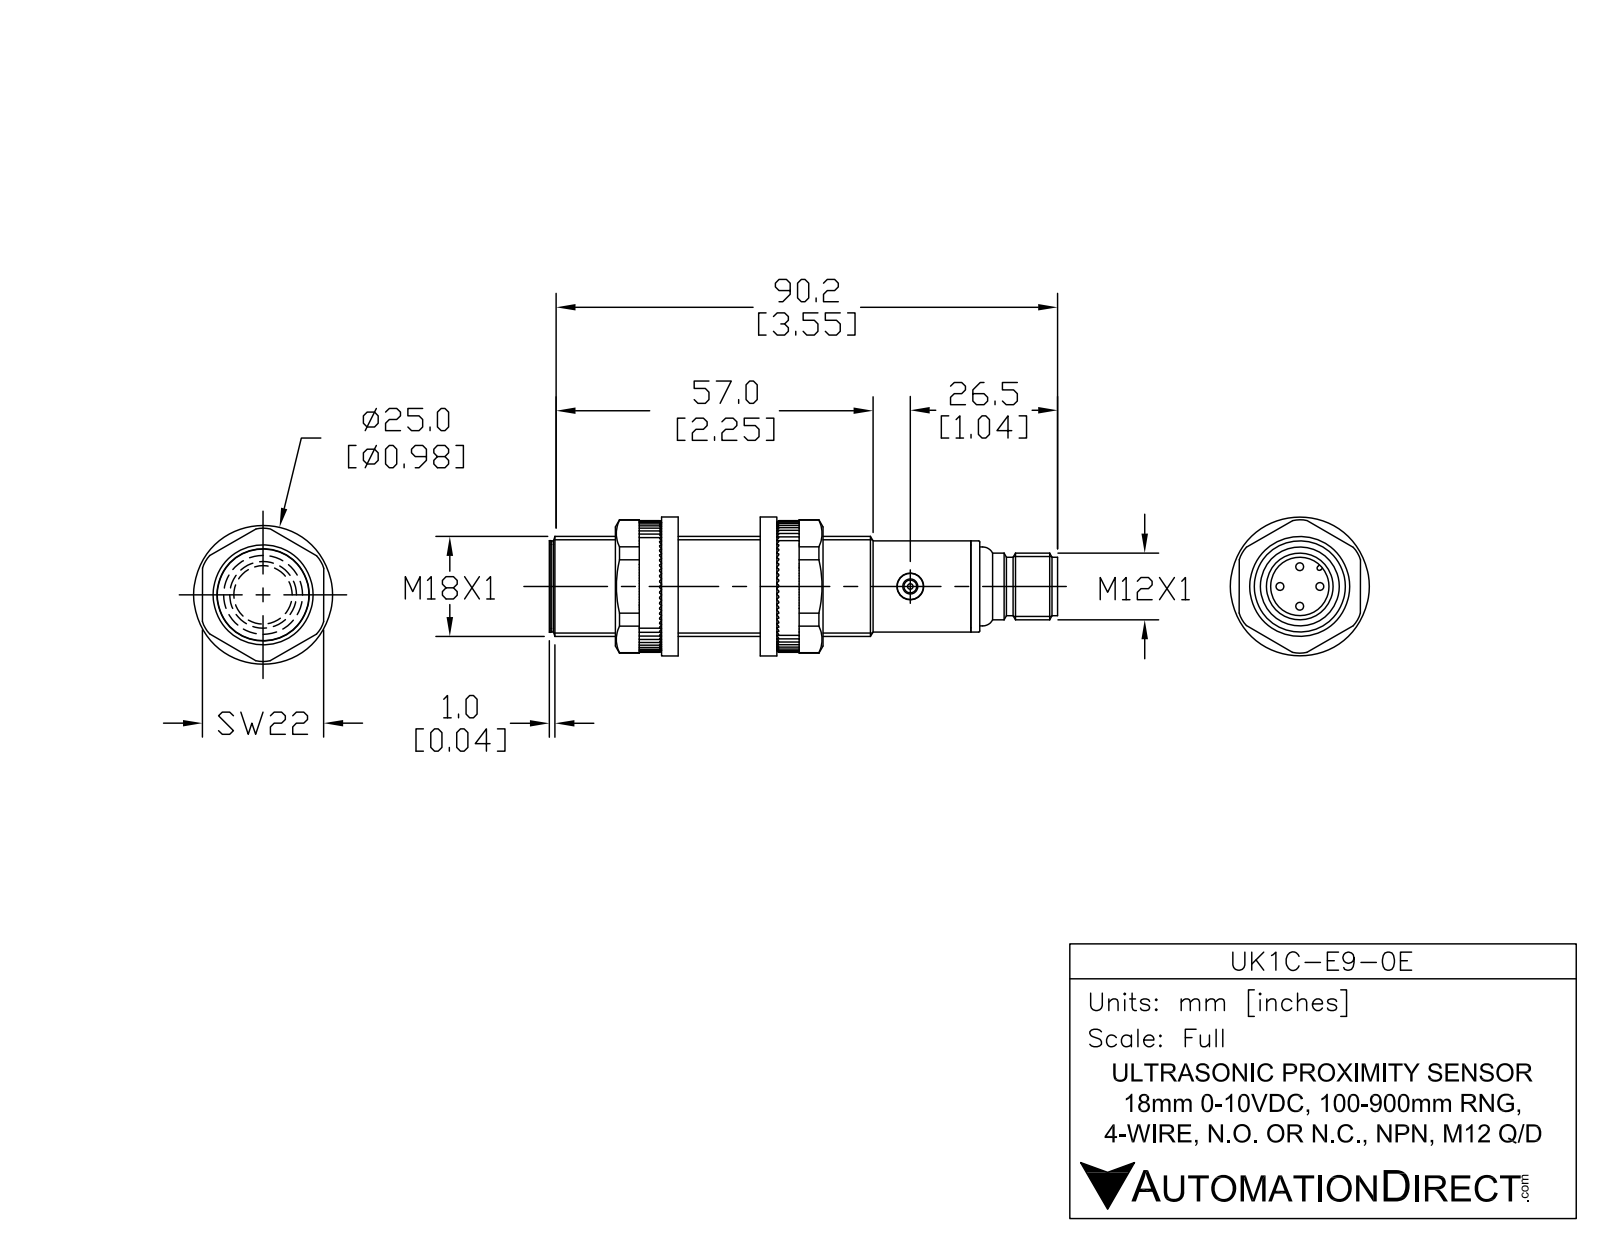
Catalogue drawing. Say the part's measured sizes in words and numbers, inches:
The part is named "UK1C-E9-0E". Its 3-D file was written by "SolidWorks 2017 (AUTOMOTIVE_DESIGN)". It is 6 solids with 106 faces: 21 planar, 48 cylindrical and 37 other. Overall it measures 3.606 by 0.709 by 0.709 inches. Its volume is 1.202 cubic inches and its surface area 10.68 square inches. Round holes: 1 of diameter 0.106, 1 of diameter 0.185, 1 of diameter 0.276, 1 of diameter 0.327, 1 of diameter 0.374. Round bosses or shafts: 4 of diameter 0.039, 1 of diameter 0.709, 1 of diameter 0.654, 1 of diameter 0.646, 1 of diameter 0.622, 1 of diameter 0.559, 1 of diameter 0.472, 1 of diameter 0.413. Partial cylindrical surfaces (rounded edges, fillets, slot ends): 1 of radius 0.024. The main face-to-face distances are 2.957, 0.039, 2.996, 0.037, 2.994, 0.043, 0.157, 3.055, 3.053, 3.016.
